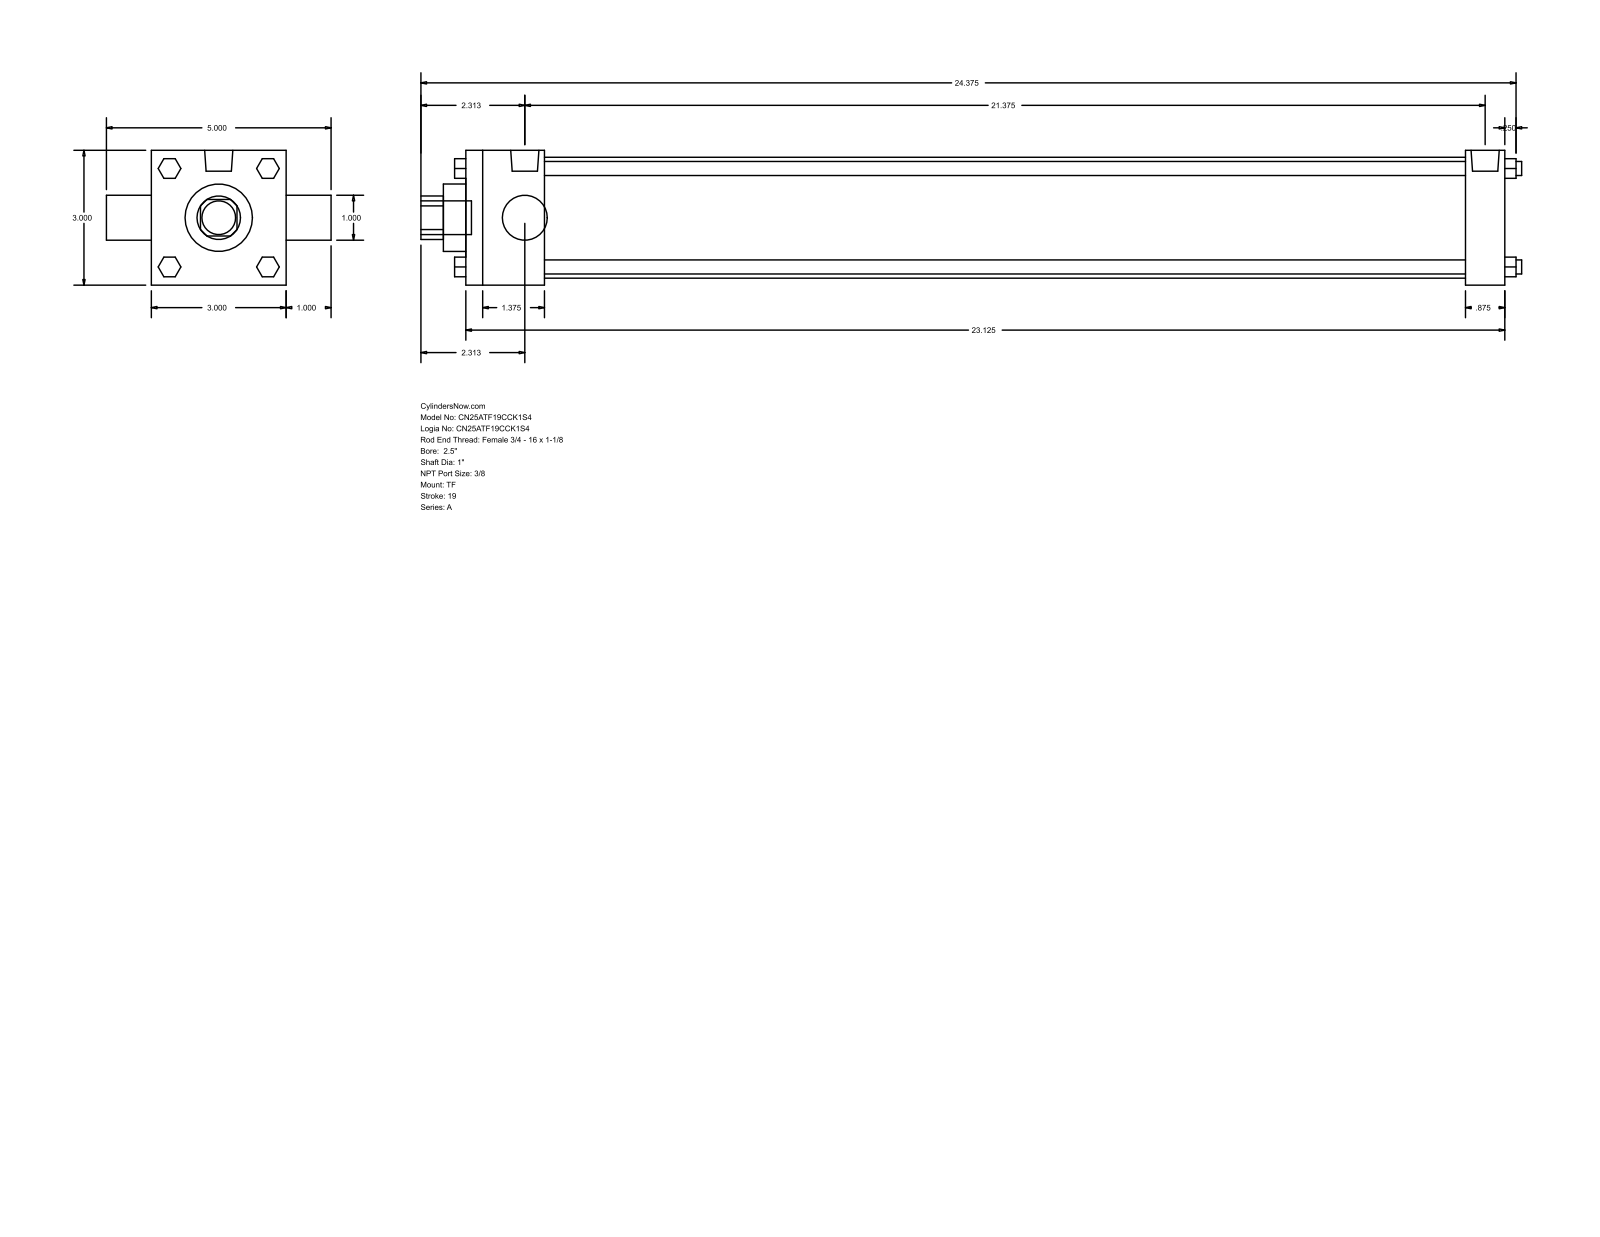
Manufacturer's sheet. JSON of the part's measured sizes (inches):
{"part_name": "A_TF__0250_1", "step_written_by": "GSSL Pune (CONFIG_CONTROL_DESIGN)", "units": "inches", "bodies": {"solids": 0, "faces": 120, "planar": 92, "cylindrical": 28, "other": 0}, "overall_size": [24.5, 5, 3], "round_holes": [[1, 2], [1.5, 1], [2.69, 1]], "round_bosses_or_shafts": [[0.313, 4], [0.219, 3], [0.627, 2], [0.75, 1]], "partial_cylinders_radius": [[0.484, 1]], "face_to_face_distances": [3, 23.125, 1.75, 22.25, 20.5, 21.375, 0.875, 1, 4, 23.625]}
